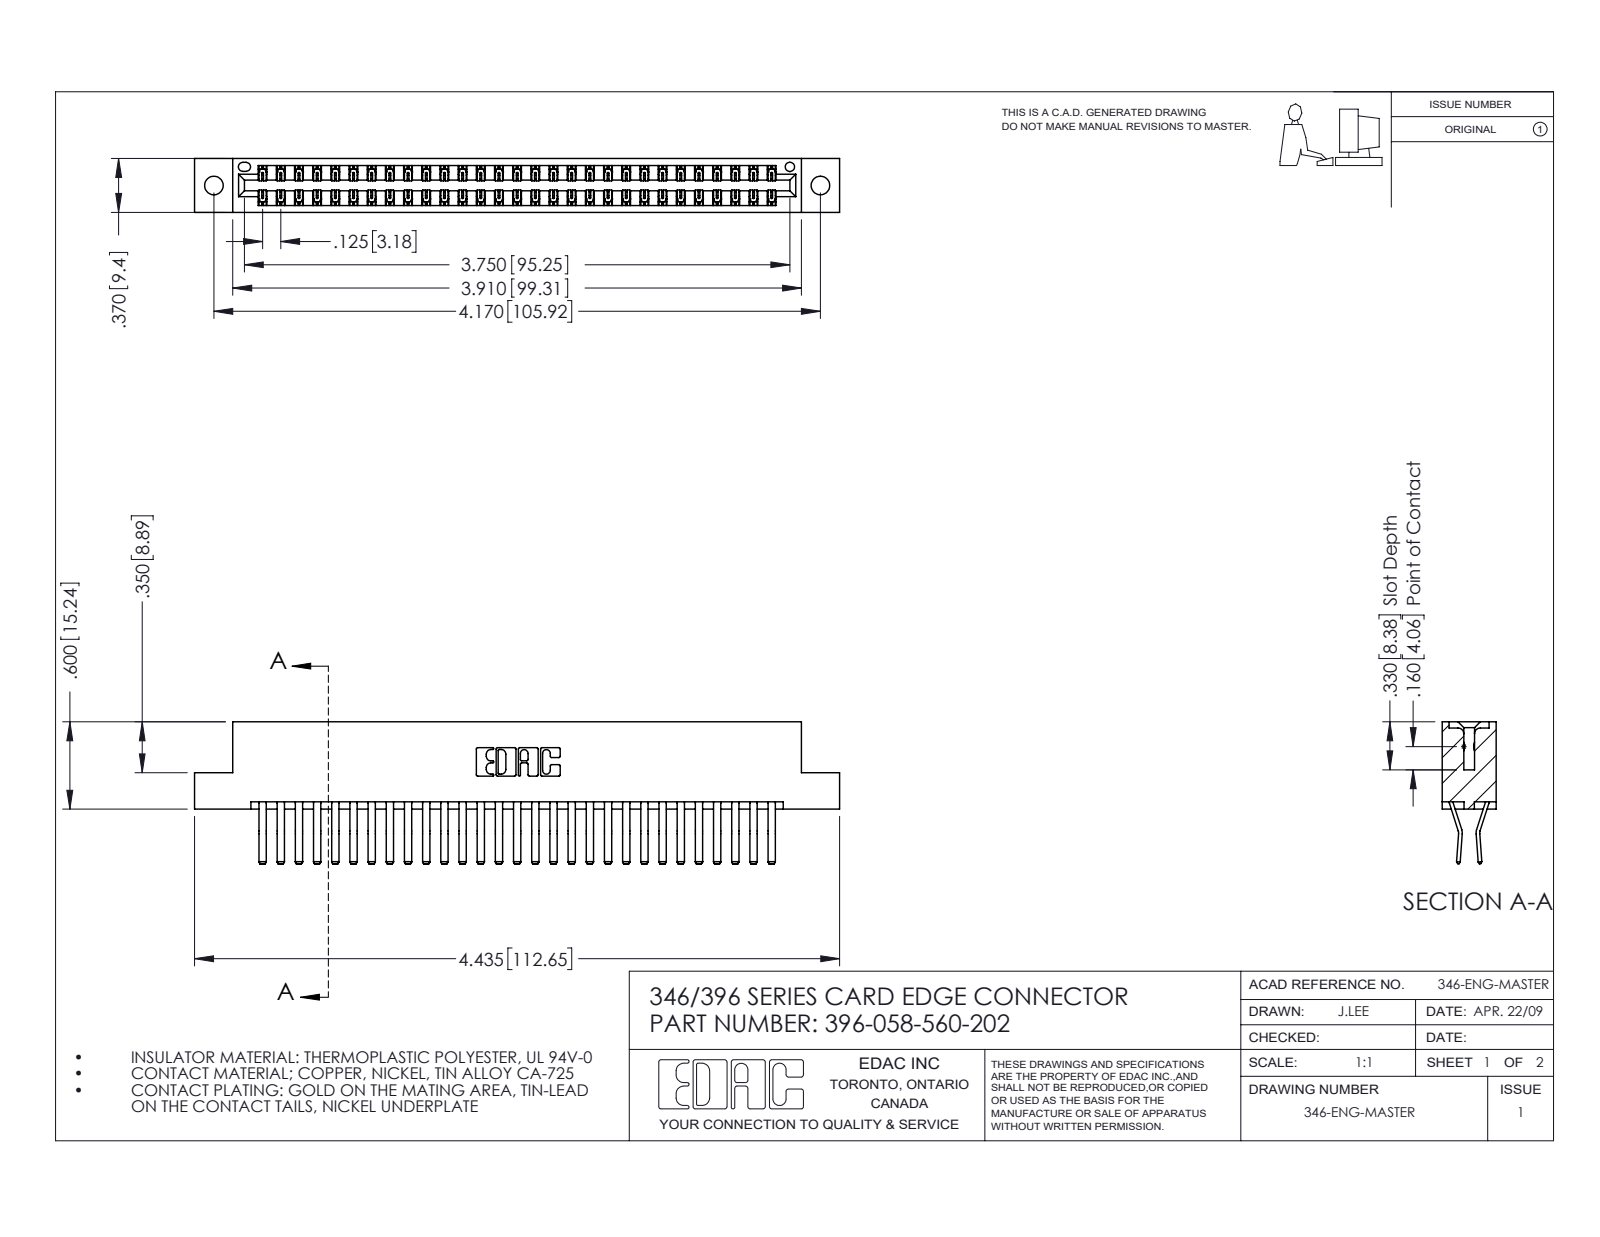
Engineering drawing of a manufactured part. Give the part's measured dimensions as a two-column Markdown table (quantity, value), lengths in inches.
| quantity | value |
| --- | --- |
| part name | 346 Part_Flush Mounting Lugs - 0.128 Dia; 396-058-560-202; 345-292-001_560 Tail |
| STEP written by | SolidWorks 2016 (CONFIG_CONTROL_DESIGN) |
| units | inches |
| bodies | 59 solids, 3254 faces (2106 planar, 1148 cylindrical, 0 other) |
| overall size | 4.435 × 0.975 × 0.37 |
| volume | 0.685 in³ |
| surface area | 24.76 in² |
| round holes (diameter × count) | 0.128 × 2, 0.064 × 1 |
| partial cylindrical surfaces (radius × count) | 0.006 × 87, 0.01 × 22, 0.007 × 6, 0.031 × 6, 0.026 × 3, 0.01 × 2, 0.014 × 2, 0.022 × 2 |
| main face-to-face distances | 0.048, 0.322, 0.37, 0.25, 0.025, 0.072, 0.298, 0.275, 0.148, 0.222 |
| hole center spacings | 0.246, 3.962, 4.17 |
